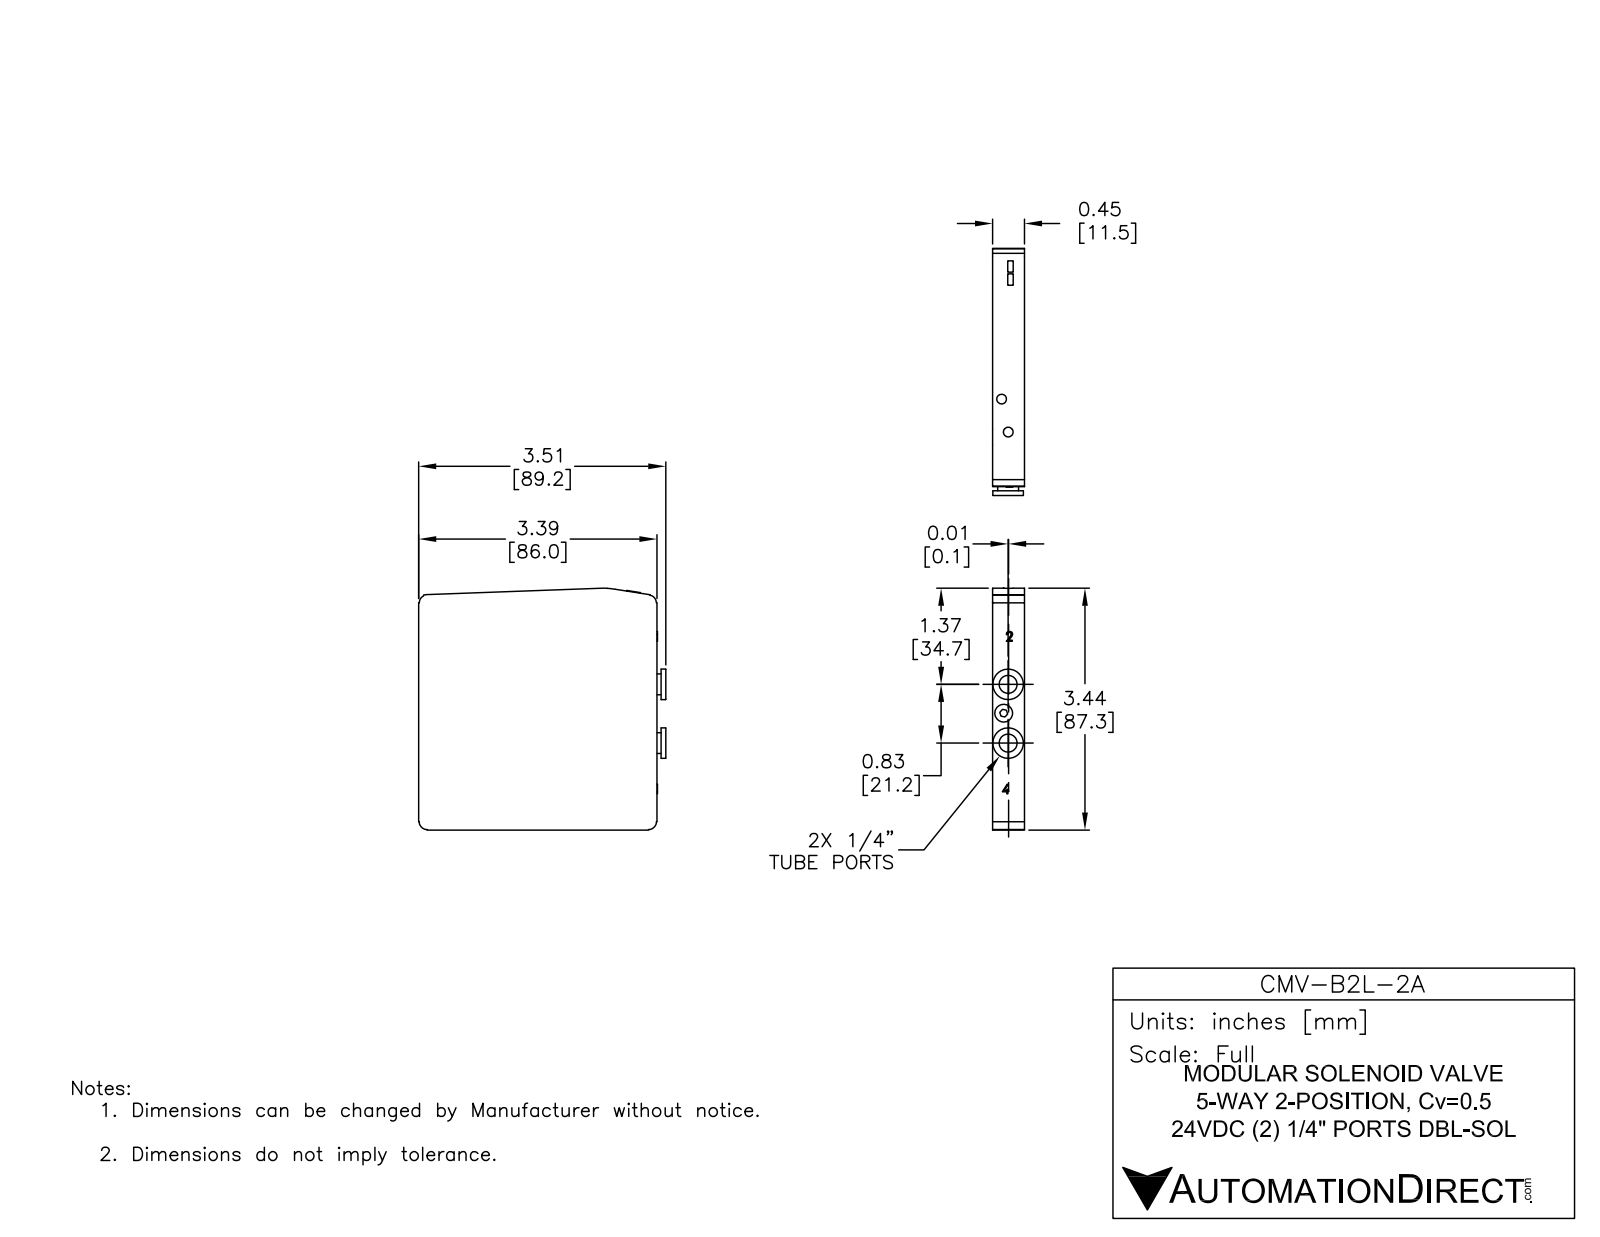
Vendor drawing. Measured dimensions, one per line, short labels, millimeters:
name: CMV-B2L-2A
written by: SolidWorks 2013 (AUTOMOTIVE_DESIGN)
unit: mm
bodies: 78 solids, 1153 faces (880 planar, 162 cylindrical, 111 other)
size: 89.5 × 87.3 × 20.43
volume: 78 068 mm³; area: 44 225 mm²
holes: 4× ⌀5.25, 4× ⌀6.5, 2× ⌀3.35, 2× ⌀4.4, 2× ⌀8, 2× ⌀9.5, 1× ⌀3.6, 1× ⌀6.25, 1× ⌀6.4
bosses: 4× ⌀1.5, 2× ⌀10.8, 2× ⌀7.75, 2× ⌀6.25, 2× ⌀5.75, 2× ⌀4.2, 2× ⌀4, 1× ⌀3.5
rounds: 12× R2.35, 4× R0.78, 4× R1.5, 4× R2.8, 2× R0.15, 2× R0.25, 2× R1, 2× R2.25
face distances: 11.5, 1.5, 10, 1, 3, 83, 2.5, 12.5, 10.83, 11.83
hole spacings: 9.7, 19.83, 22.17, 8.66, 8.68, 9.46, 10.38, 10.63
